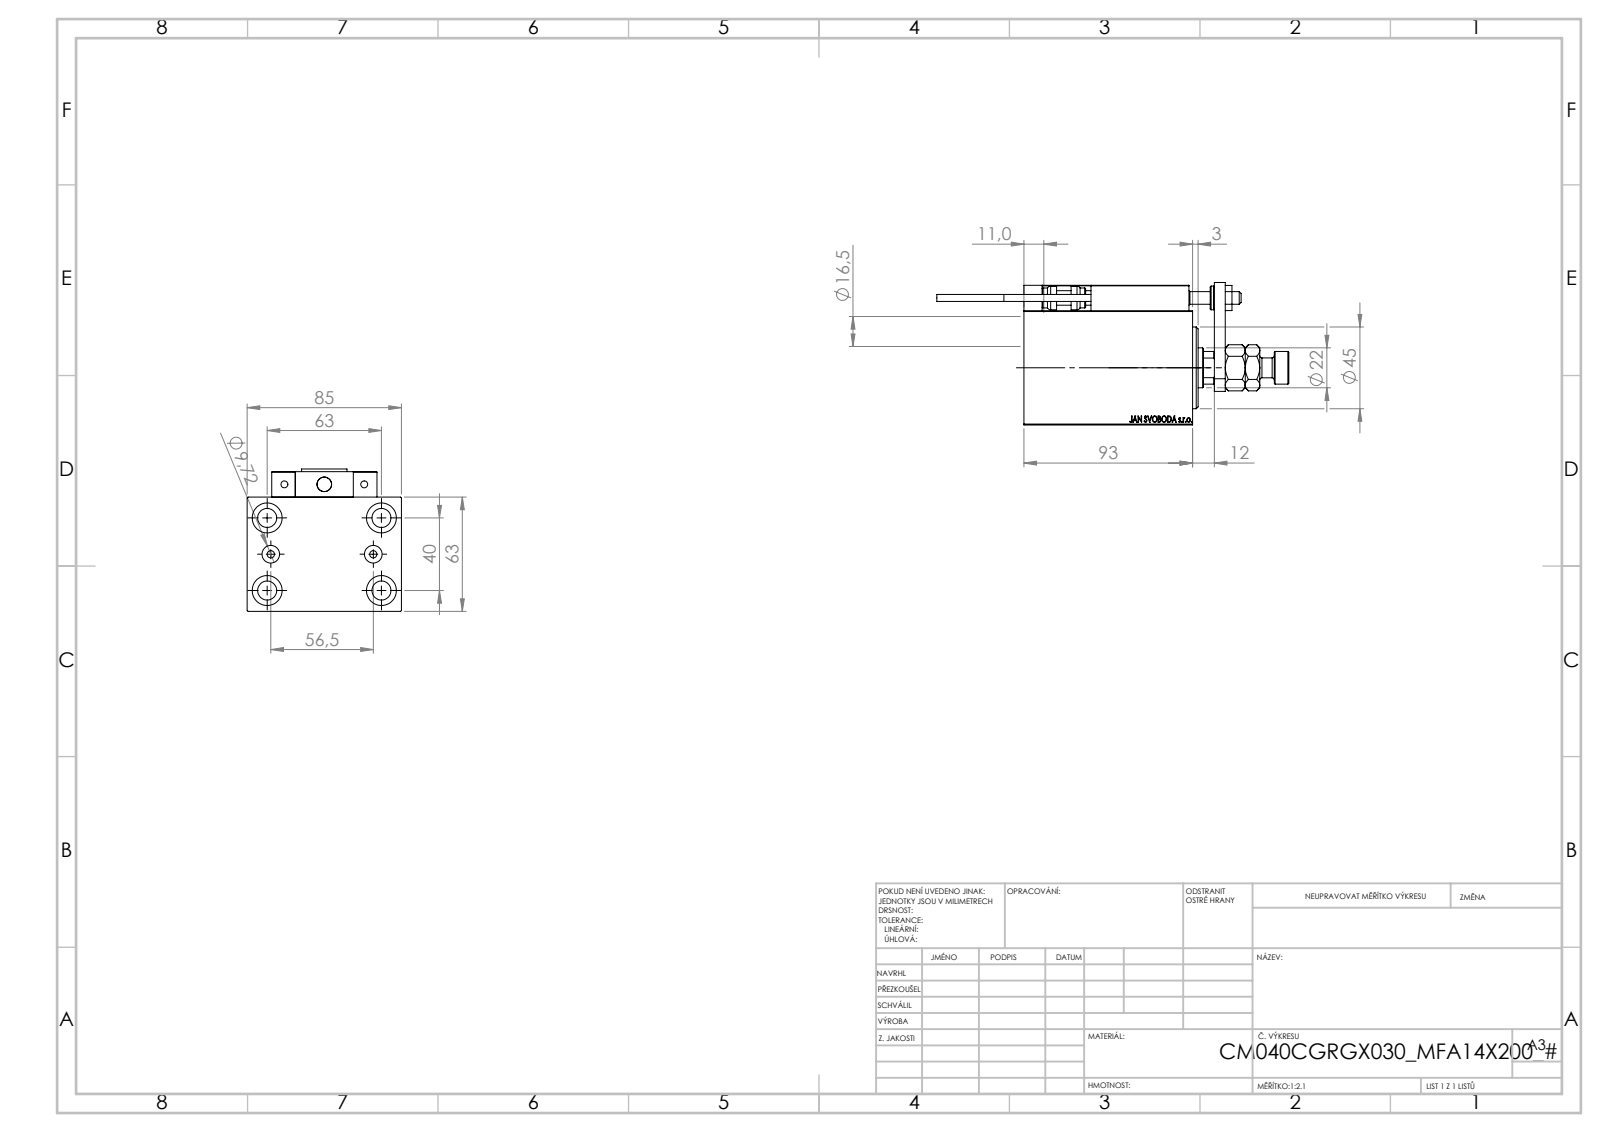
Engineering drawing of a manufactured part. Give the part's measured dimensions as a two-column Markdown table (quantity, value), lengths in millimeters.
| quantity | value |
| --- | --- |
| part name | SWITCH DIM B,W; X_Y_MFA; TYC_L79; SWITCH_X_FRONT_BACK (+8 more) |
| STEP written by | SolidWorks 2019 (CONFIG_CONTROL_DESIGN) |
| units | millimeters |
| bodies | 24 solids, 1330 faces (576 planar, 188 cylindrical, 566 other) |
| overall size | 194 × 85 × 78.5 |
| volume | 489 338 mm³ |
| surface area | 109 615 mm² |
| round holes (diameter × count) | 4 × 6, 8 × 5, 16.5 × 5, 3.2 × 4, 10.5 × 4, 5 × 2, 9.72 × 2, 7 × 1, 12.5 × 1, 22 × 1, 25.5 × 1, 40 × 1 |
| round bosses / shafts (diameter × count) | 11 × 2, 5 × 2, 3.8 × 2, 18 × 1, 13 × 1 |
| partial cylindrical surfaces (radius × count) | 0.3 × 30, 3 × 2, 10.5 × 1 |
| main face-to-face distances | 63, 85, 12, 81, 93, 14, 30, 18, 77, 45 |
| hole center spacings | 37.31, 11.37, 20, 20.1, 20.5, 29.59, 29.69, 36.06 |
